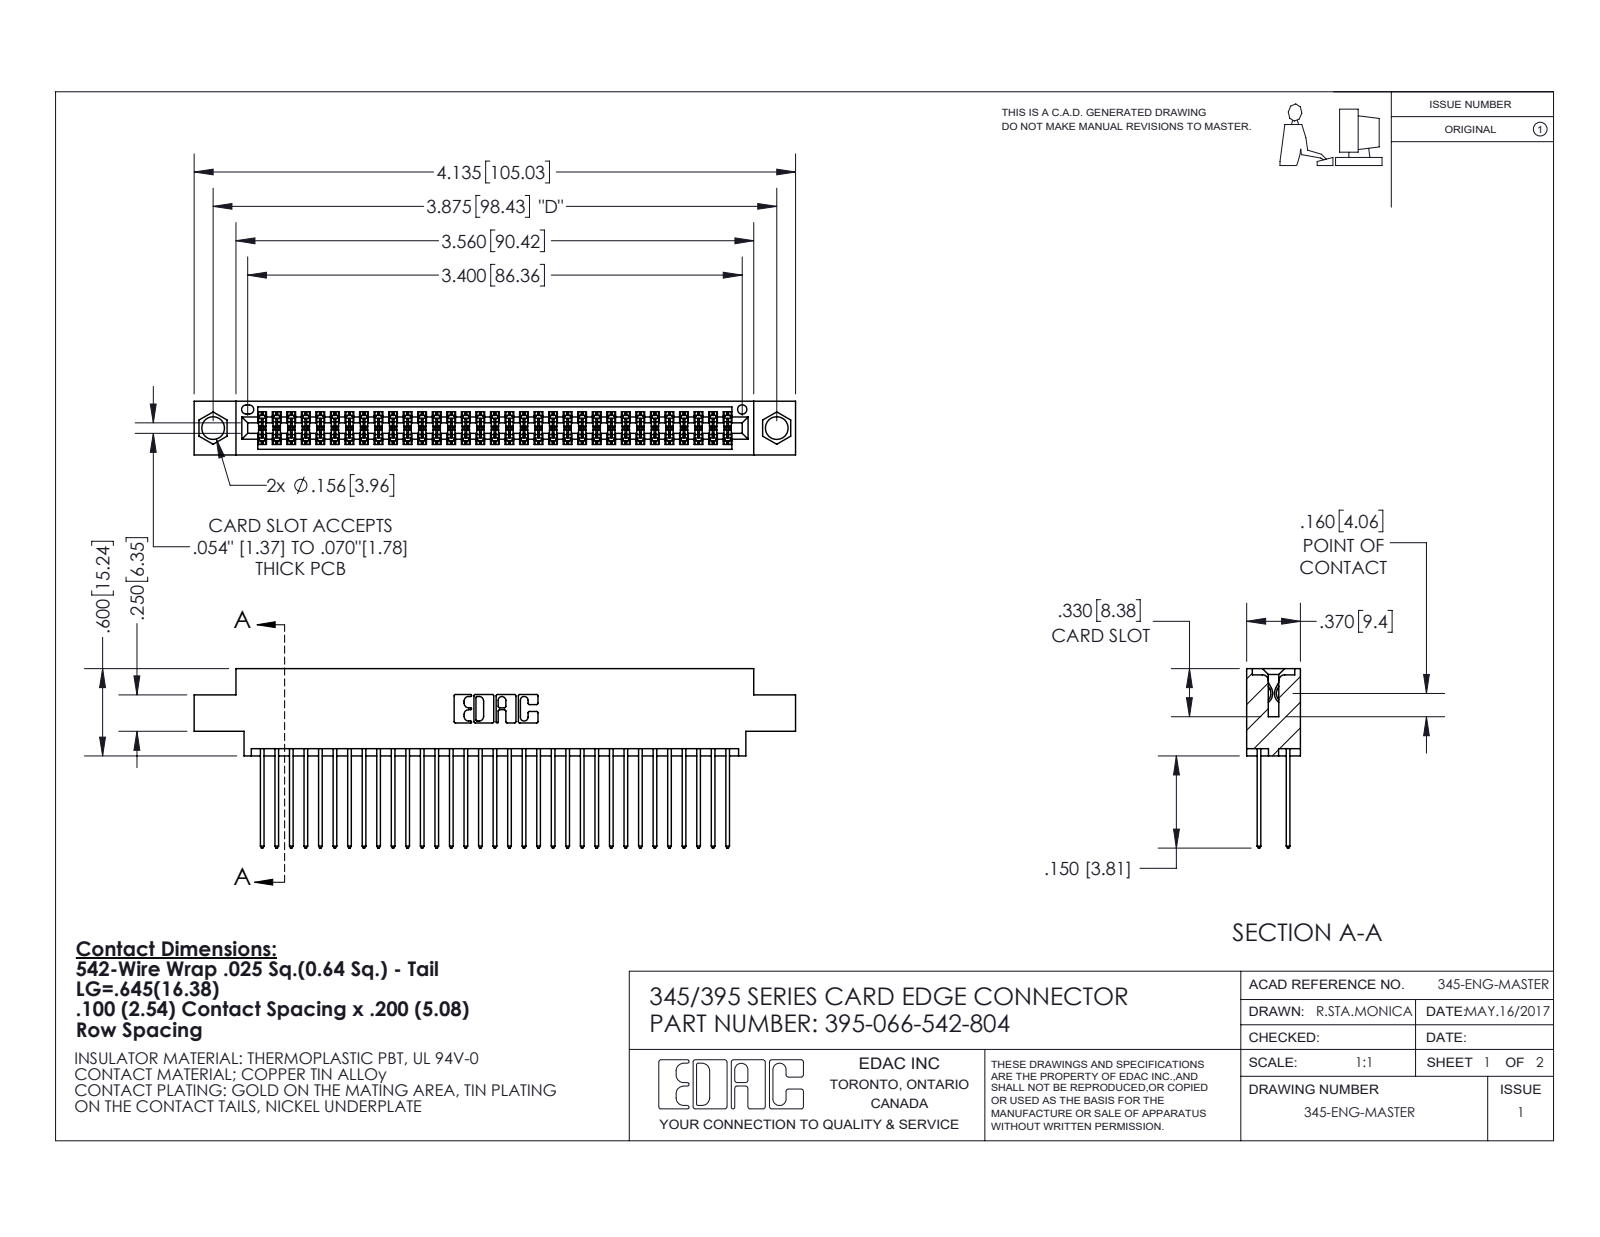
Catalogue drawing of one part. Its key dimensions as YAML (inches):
part_name: "345-292-001_345-293-142; 345 Part_0.170 Offset - 0.156 Dia-TI; 395-066-542-804"
step_written_by: "SolidWorks 2020 (CONFIG_CONTROL_DESIGN)"
units: inches
bodies: {solids: 67, faces: 3444, planar: 2276, cylindrical: 1168, other: 0}
overall_size: [4.135, 1.232, 0.37]
volume: 0.623
surface_area: 25.34
round_holes:
  - {diameter: 0.156, count: 2}
  - {diameter: 0.064, count: 1}
partial_cylinders:
  - {radius: 0.006, count: 132}
  - {radius: 0.01, count: 66}
  - {radius: 0.01, count: 22}
  - {radius: 0.007, count: 6}
  - {radius: 0.031, count: 6}
  - {radius: 0.026, count: 3}
  - {radius: 0.014, count: 2}
  - {radius: 0.019, count: 2}
face_to_face_distances: [0.072, 0.298, 0.2, 0.098, 0.272, 0.025, 0.37, 0.225, 0.175, 0.149]
hole_center_spacings: [0.27, 3.64, 3.875]
